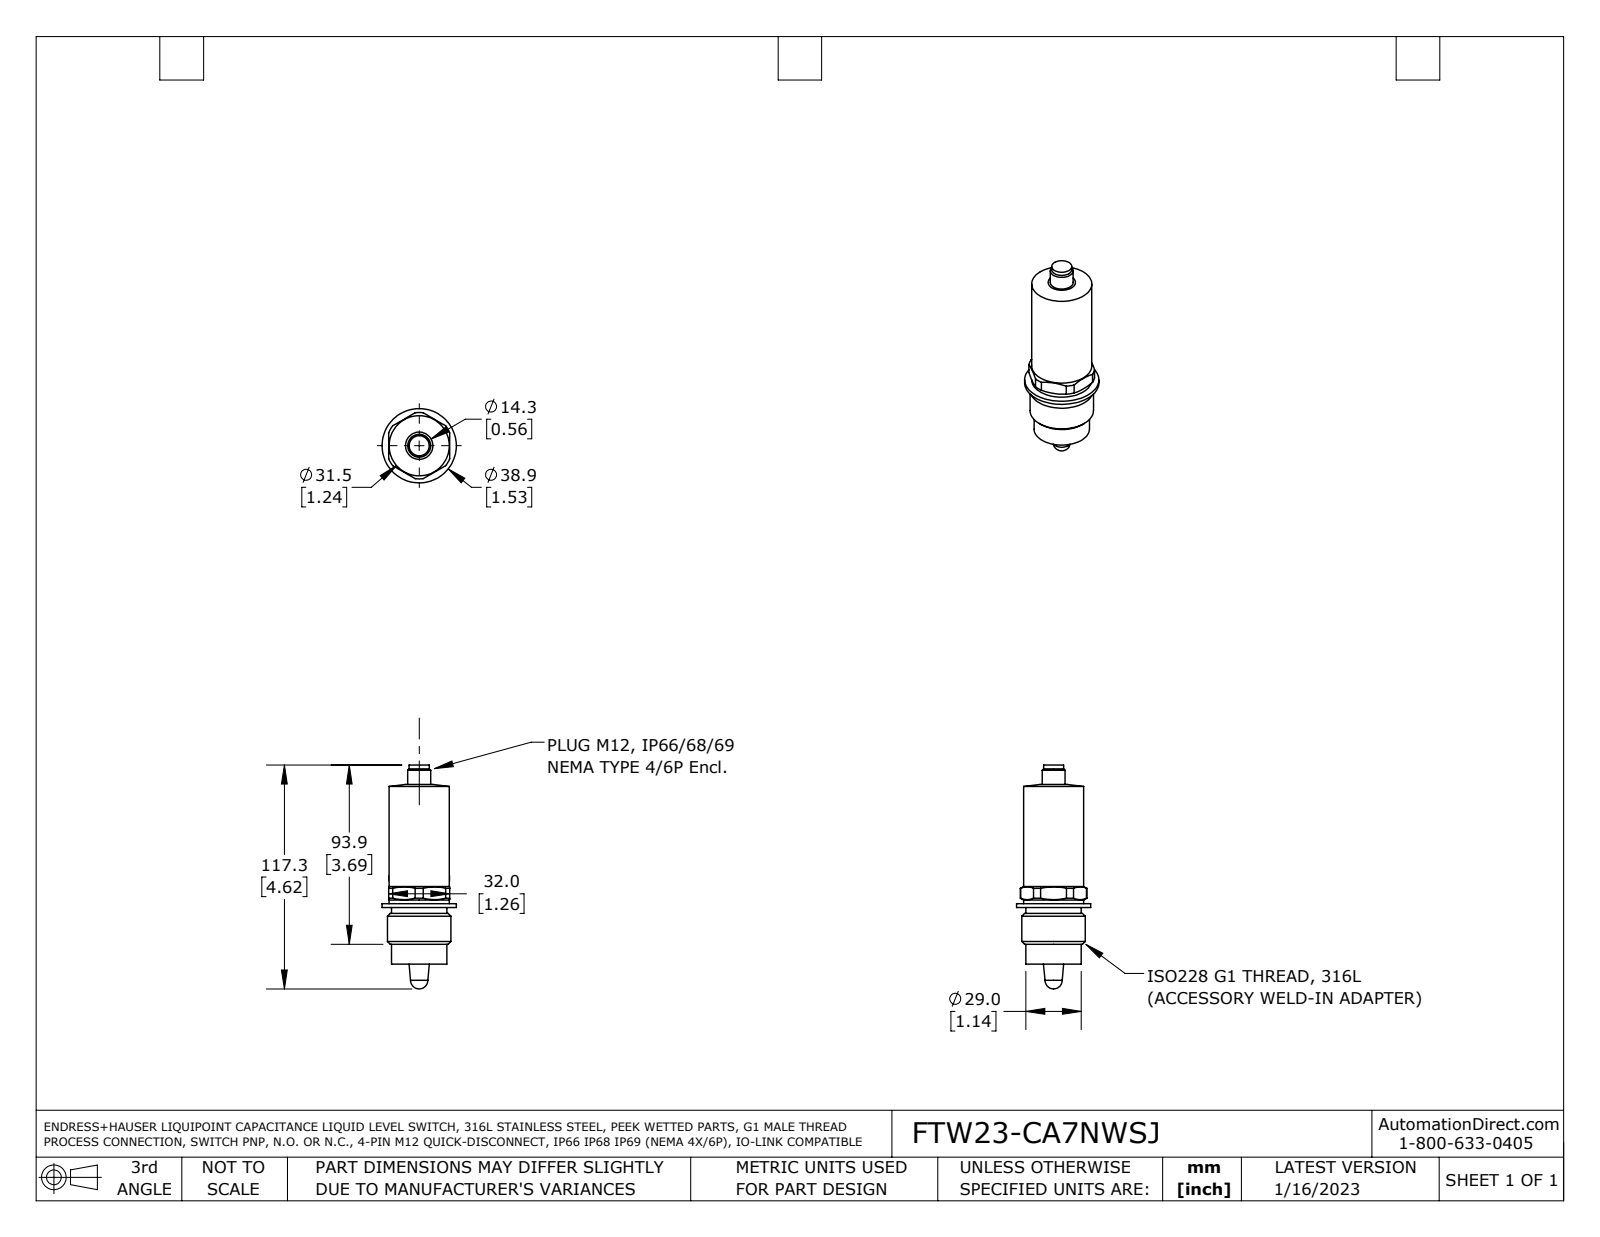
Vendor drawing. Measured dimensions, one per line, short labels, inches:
name: FTW23-CA7NWSJ-Endress HauserConsultAG-3D-08-31-2022
written by: SolidWorks 2021 (AUTOMOTIVE_DESIGN)
unit: in
bodies: 1 solid, 50 faces (13 planar, 22 cylindrical, 15 other)
size: 4.609 × 1.531 × 1.531
volume: 4.632 in³; area: 19.63 in²
bosses: 1× ⌀1.531, 1× ⌀1.309, 1× ⌀1.24, 1× ⌀1.142, 1× ⌀0.472, 1× ⌀0.413
rounds: 1× R0.684
face distances: 1.165, 1.244, 0.079, 1.26, 4.104, 2.939, 2.86, 1.047, 0.118, 0.197
